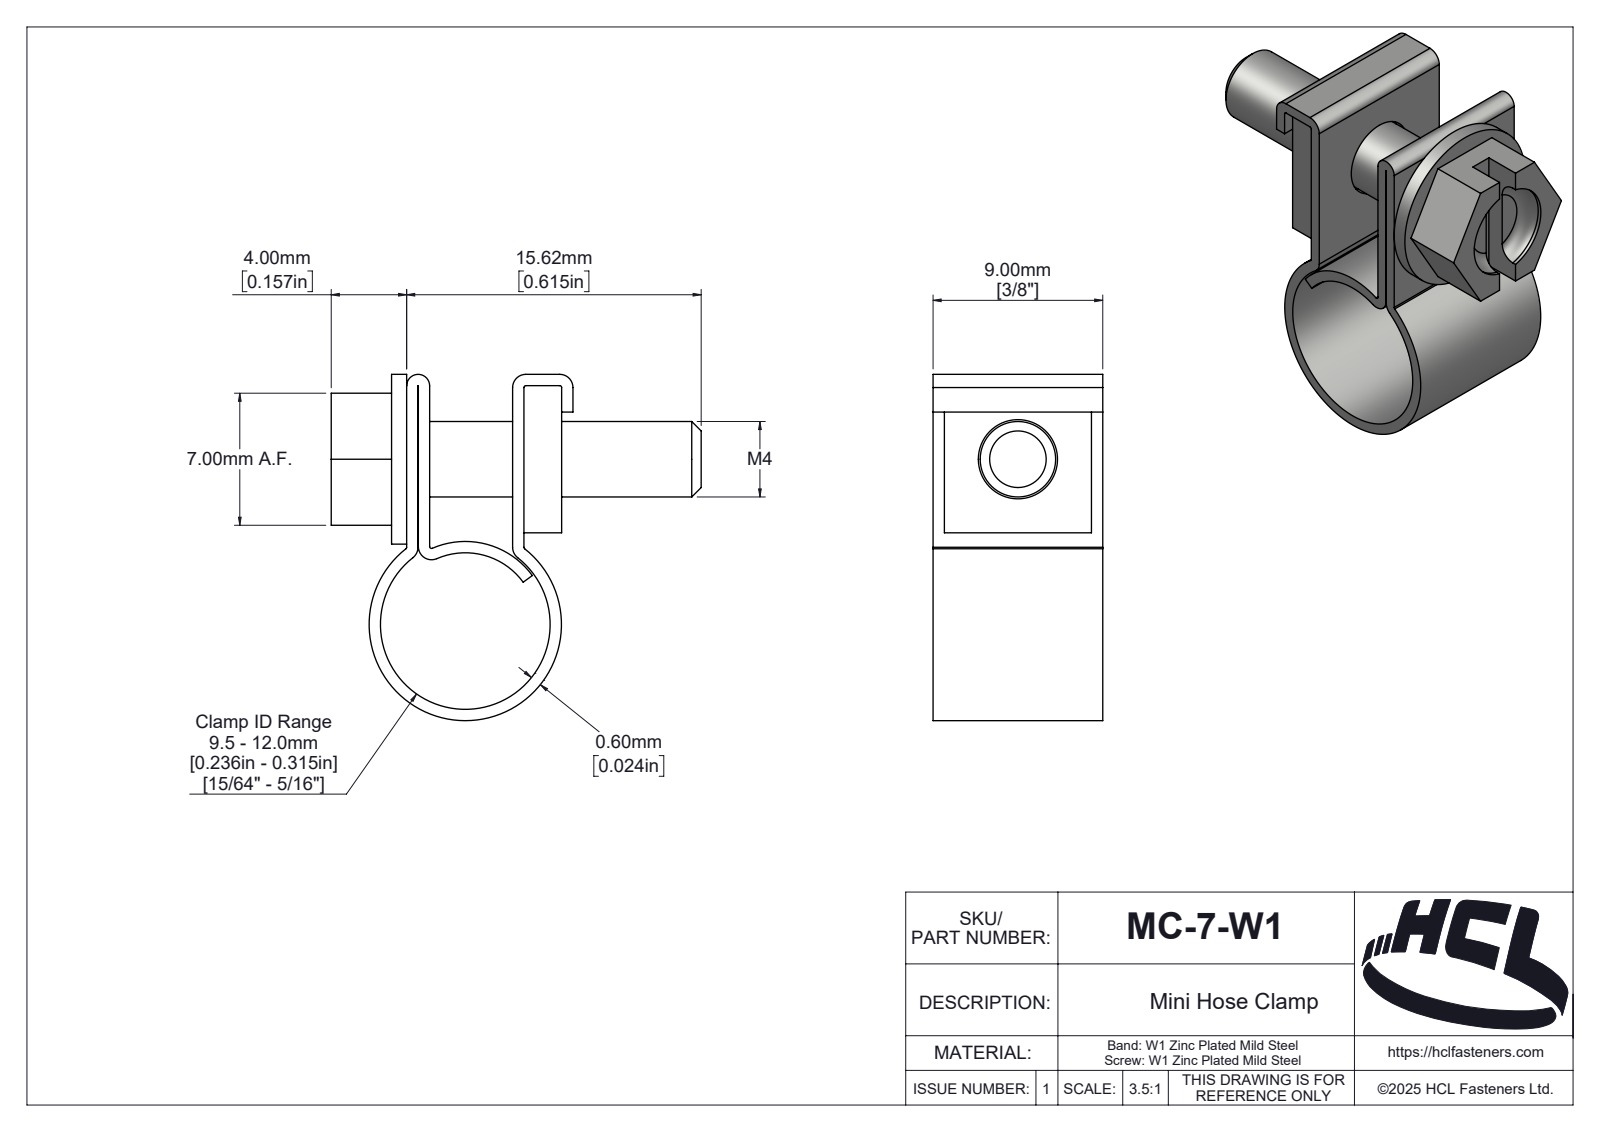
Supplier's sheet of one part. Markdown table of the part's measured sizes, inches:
| quantity | value |
| --- | --- |
| part name | MC-7-W1 |
| STEP written by | SolidWorks 2025 (AUTOMOTIVE_DESIGN) |
| units | inches |
| bodies | 3 solids, 175 faces (38 planar, 84 cylindrical, 53 other) |
| overall size | 0.772 × 0.723 × 0.354 |
| volume | 0.046 in³ |
| surface area | 2.736 in² |
| round holes (diameter × count) | 0.165 × 1, 0.197 × 1 |
| round bosses / shafts (diameter × count) | 0.354 × 1, 0.157 × 1 |
| partial cylindrical surfaces (radius × count) | 0.004 × 5, 0.028 × 5, 0.008 × 1, 0.024 × 1, 0.032 × 1, 0.04 × 1, 0.042 × 1, 0.05 × 1 |
| main face-to-face distances | 0.024, 0.024, 0.221, 0.197, 0.245, 0.276, 0.079, 0.102, 0.324, 0.299 |
